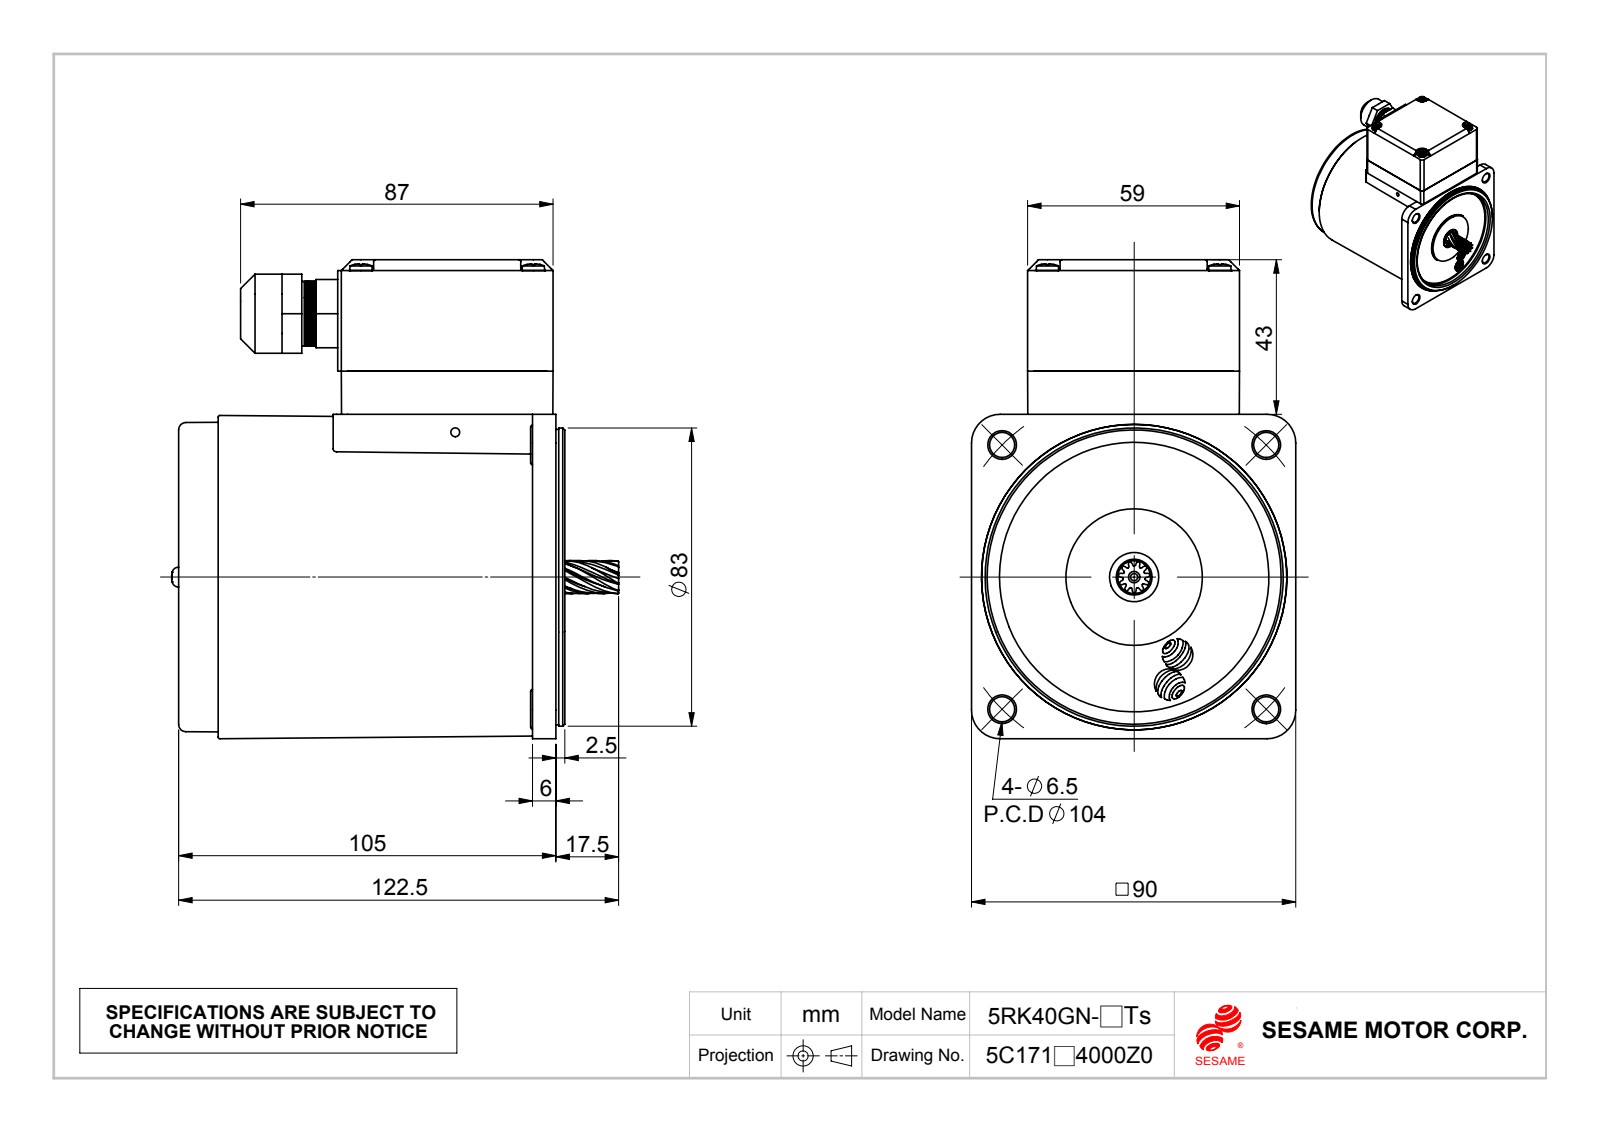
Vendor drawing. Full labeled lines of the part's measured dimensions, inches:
Part name (STEP PRODUCT): M540Ts-RK; 成品180度; Ts下墊片; 40GN (+1 more)
STEP written by: SolidWorks 2010 (CONFIG_CONTROL_DESIGN)
Units: inches
Bodies: 14 solids, 2660 faces (240 planar, 977 cylindrical, 1443 other)
Overall size (bounding box): 5.248 × 4.9 × 3.555
Volume: 18.75 in³ · Surface area: 199.9 in²
Round holes (diameter × count): ⌀0.13 ×4, ⌀0.138 ×4, ⌀0.154 ×4, ⌀0.169 ×4, ⌀0.244 ×4, ⌀0.276 ×4, ⌀0.098 ×3, ⌀0.157 ×2, ⌀0.079 ×1, ⌀0.433 ×1, ⌀0.472 ×1, ⌀0.539 ×1
Round bosses / shafts (diameter × count): ⌀0.118 ×6, ⌀0.248 ×4, ⌀0.217 ×2, ⌀3.316 ×1, ⌀3.268 ×1, ⌀3.236 ×1, ⌀1.772 ×1, ⌀1.496 ×1
Partial cylindrical surfaces — rounded edges, fillets, slot ends (radius × count): R0.079 ×12, R0.012 ×8, R0.02 ×8, R0.031 ×8, R0.059 ×8, R0.065 ×8, R0.115 ×8, R0.157 ×6
Main face-to-face distances: 0.039, 4.035, 0.472, 3.858, 3.996, 0.177, 0.138, 4.075, 0.059, 0.098
Hole centre spacings: 2.16, 0.527, 0.689, 0.974, 1.273, 1.359, 1.634, 1.89
